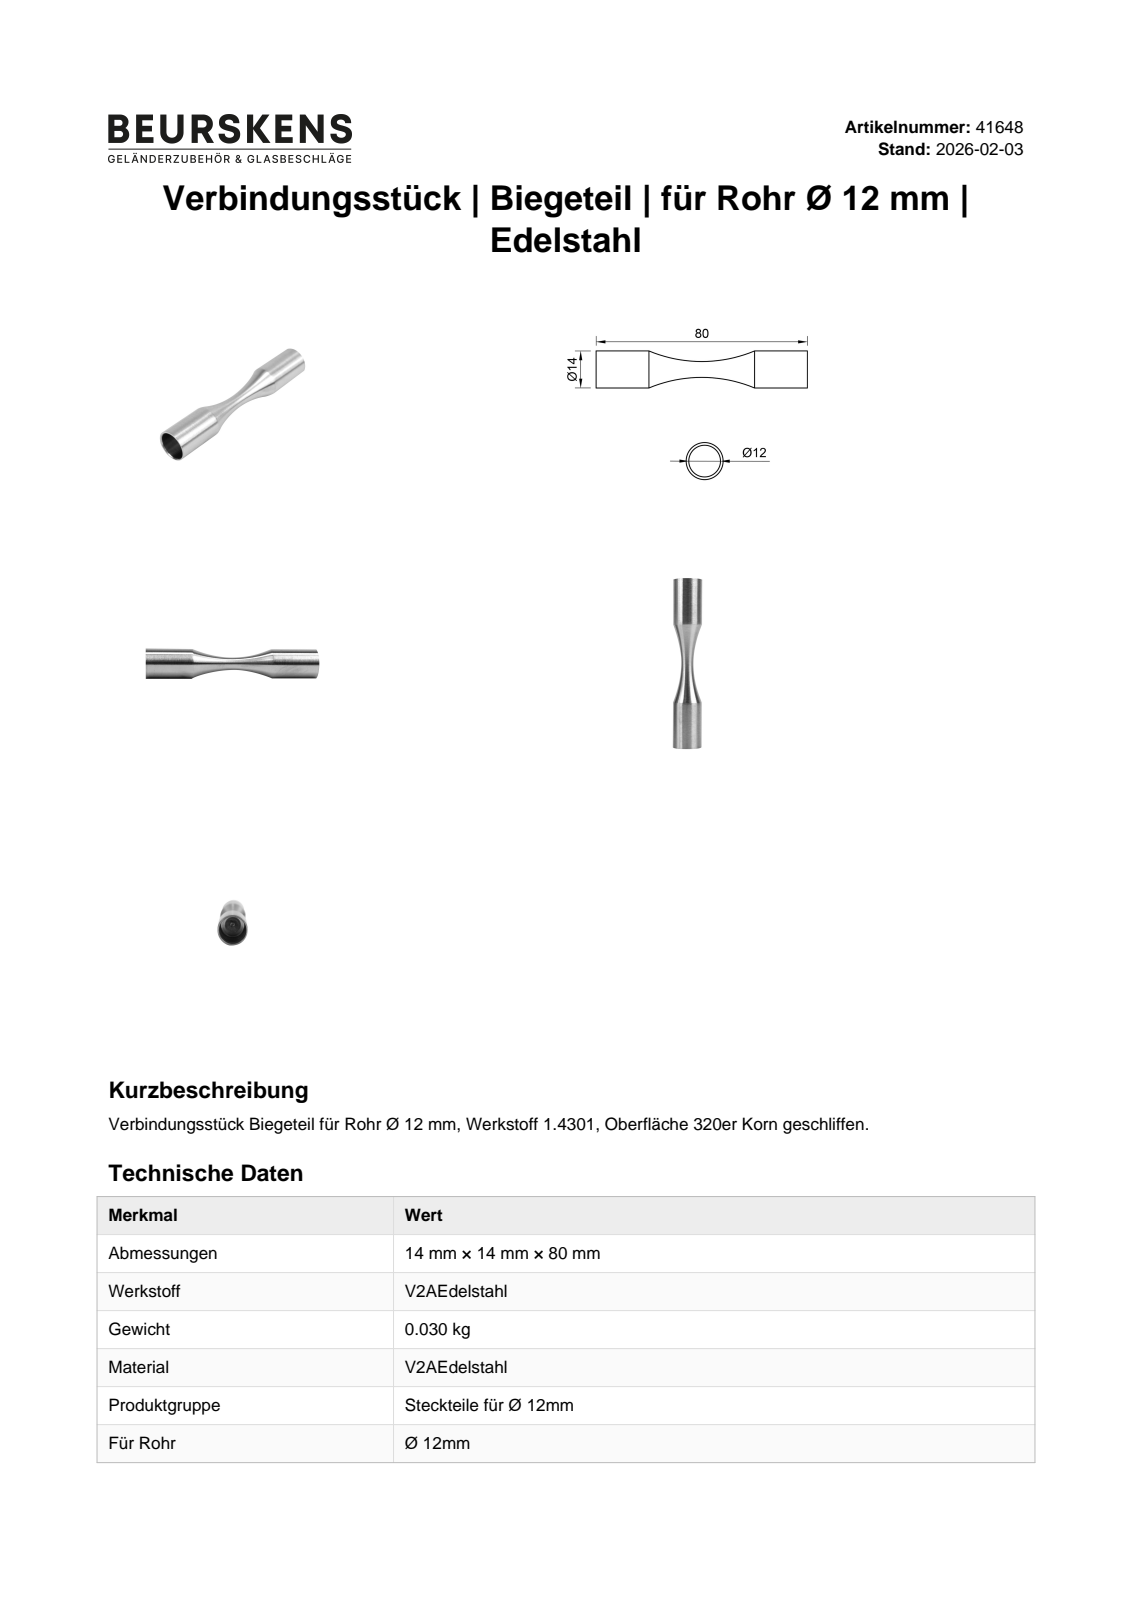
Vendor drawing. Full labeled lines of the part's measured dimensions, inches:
Part name (STEP PRODUCT): 41648-gerade
STEP written by: Autodesk Inventor 2022 (AUTOMOTIVE_DESIGN)
Units: inches
Bodies: 1 solid, 9 faces (4 planar, 4 cylindrical, 1 other)
Overall size (bounding box): 3.15 × 0.551 × 0.551
Volume: 0.253 in³ · Surface area: 7.277 in²
Round holes (diameter × count): ⌀0.472 ×1
Round bosses / shafts (diameter × count): ⌀0.551 ×1
Main face-to-face distances: 1.575, 0.787, 2.362, 3.15
